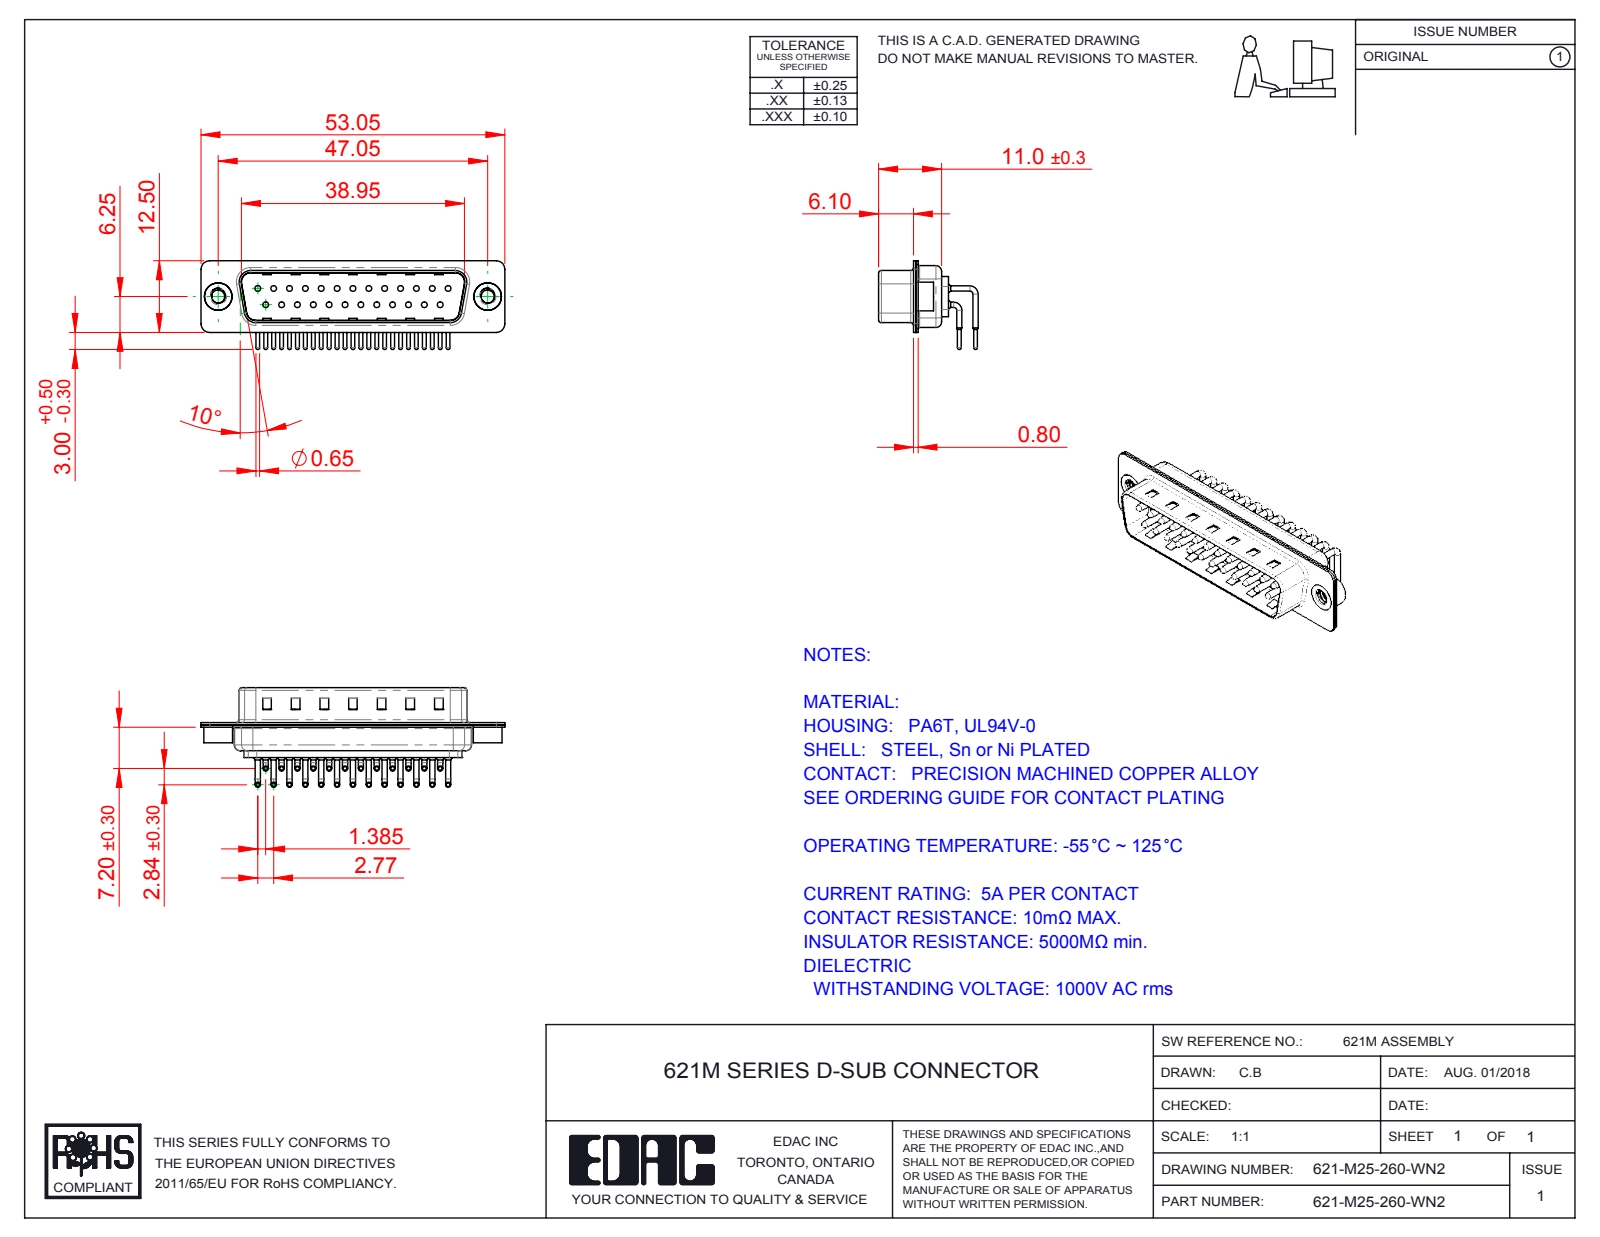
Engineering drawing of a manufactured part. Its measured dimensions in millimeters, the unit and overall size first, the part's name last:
Units: millimetres
Overall size (bounding box): 53.05 × 17.39 × 15.49
Round holes (diameter × count): ⌀1 ×25, ⌀1.7 ×25, ⌀2 ×25, ⌀2.26 ×2, ⌀4 ×2, ⌀4.8 ×2
Round bosses / shafts (diameter × count): ⌀0.9 ×50, ⌀1.5 ×25, ⌀0.65 ×25, ⌀5 ×2, ⌀4.9 ×2
Partial cylindrical surfaces — rounded edges, fillets, slot ends (radius × count): R1.01 ×25, R1.5 ×16, R2 ×12, R0.5 ×8, R1.6 ×8, R0.25 ×4, R0.6 ×4, R0.65 ×4
Main face-to-face distances: 0.4, 0.85, 9.55, 8.7, 1.25, 10.4, 1.5, 1.9, 0.35, 6.1
Hole centre spacings: 3.16, 8.31, 2.77, 5.54, 11.08, 16.62, 5.03, 5.04
Volume: 2 875 mm³ · Surface area: 7 590 mm²
Bodies: 30 solids, 3126 faces (1771 planar, 1037 cylindrical, 318 other)
Part name (STEP PRODUCT): 621-M25-260-WN2; 621M 4-40 Threaded Rivet; 621M Housing_25 Contacts; 621M Shell Rear_25 Contacts (+3 more)
STEP written by: SolidWorks 2016 (CONFIG_CONTROL_DESIGN)
